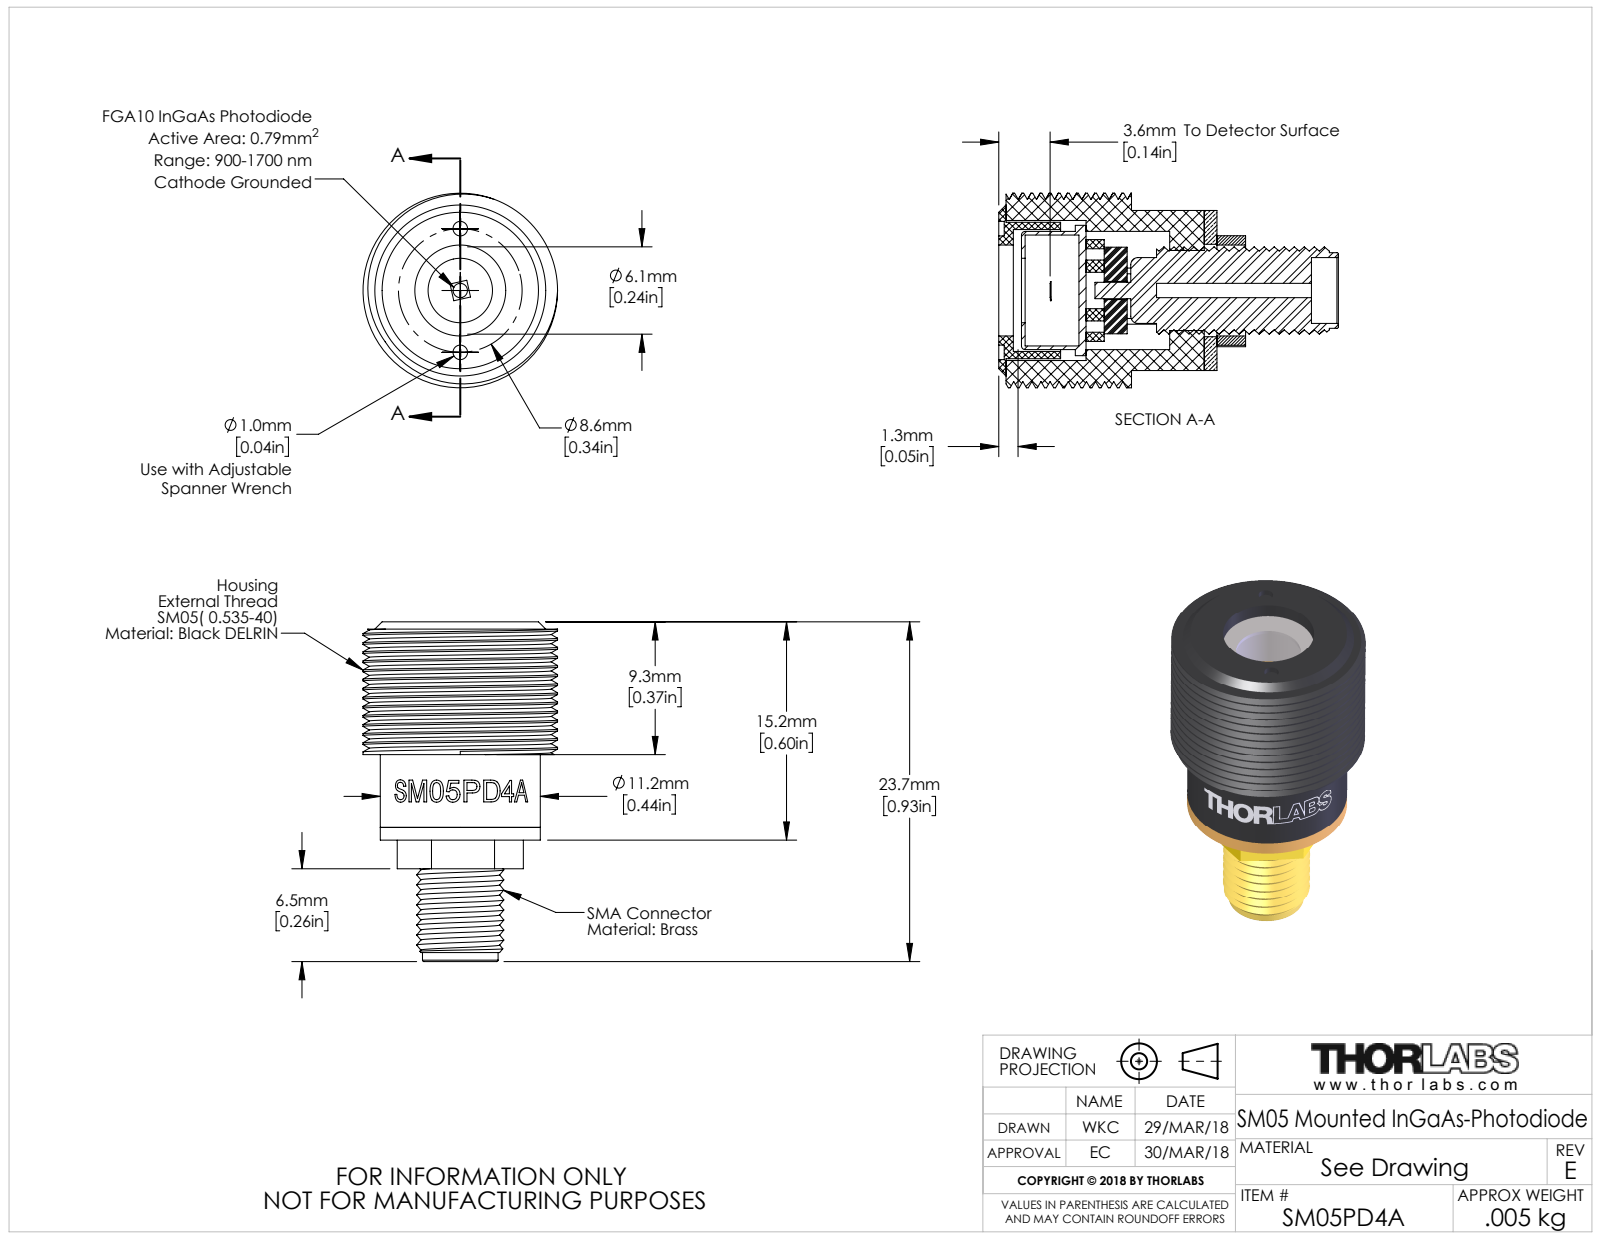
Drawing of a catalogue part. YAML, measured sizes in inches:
part_name: "8922-E0W"
step_written_by: "SolidWorks 2016 (AUTOMOTIVE_DESIGN)"
units: inches
bodies: {solids: 7, faces: 112, planar: 46, cylindrical: 52, other: 14}
overall_size: [0.924, 0.535, 0.535]
volume: 0.089
surface_area: 4.514
round_holes:
  - {diameter: 0.04, count: 2}
  - {diameter: 0.039, count: 1}
  - {diameter: 0.177, count: 1}
  - {diameter: 0.181, count: 1}
  - {diameter: 0.22, count: 1}
  - {diameter: 0.25, count: 1}
  - {diameter: 0.254, count: 1}
  - {diameter: 0.305, count: 1}
  - {diameter: 0.325, count: 1}
  - {diameter: 0.335, count: 1}
  - {diameter: 0.385, count: 1}
round_bosses_or_shafts:
  - {diameter: 0.016, count: 3}
  - {diameter: 0.535, count: 1}
  - {diameter: 0.44, count: 1}
  - {diameter: 0.375, count: 1}
  - {diameter: 0.358, count: 1}
  - {diameter: 0.325, count: 1}
  - {diameter: 0.208, count: 1}
  - {diameter: 0.045, count: 1}
face_to_face_distances: [0.335, 0.02, 0.035, 0.37, 0.58, 0.545, 0.21, 0.6, 0.565, 0.23]
hole_center_spacings: [0.17, 0.34]
